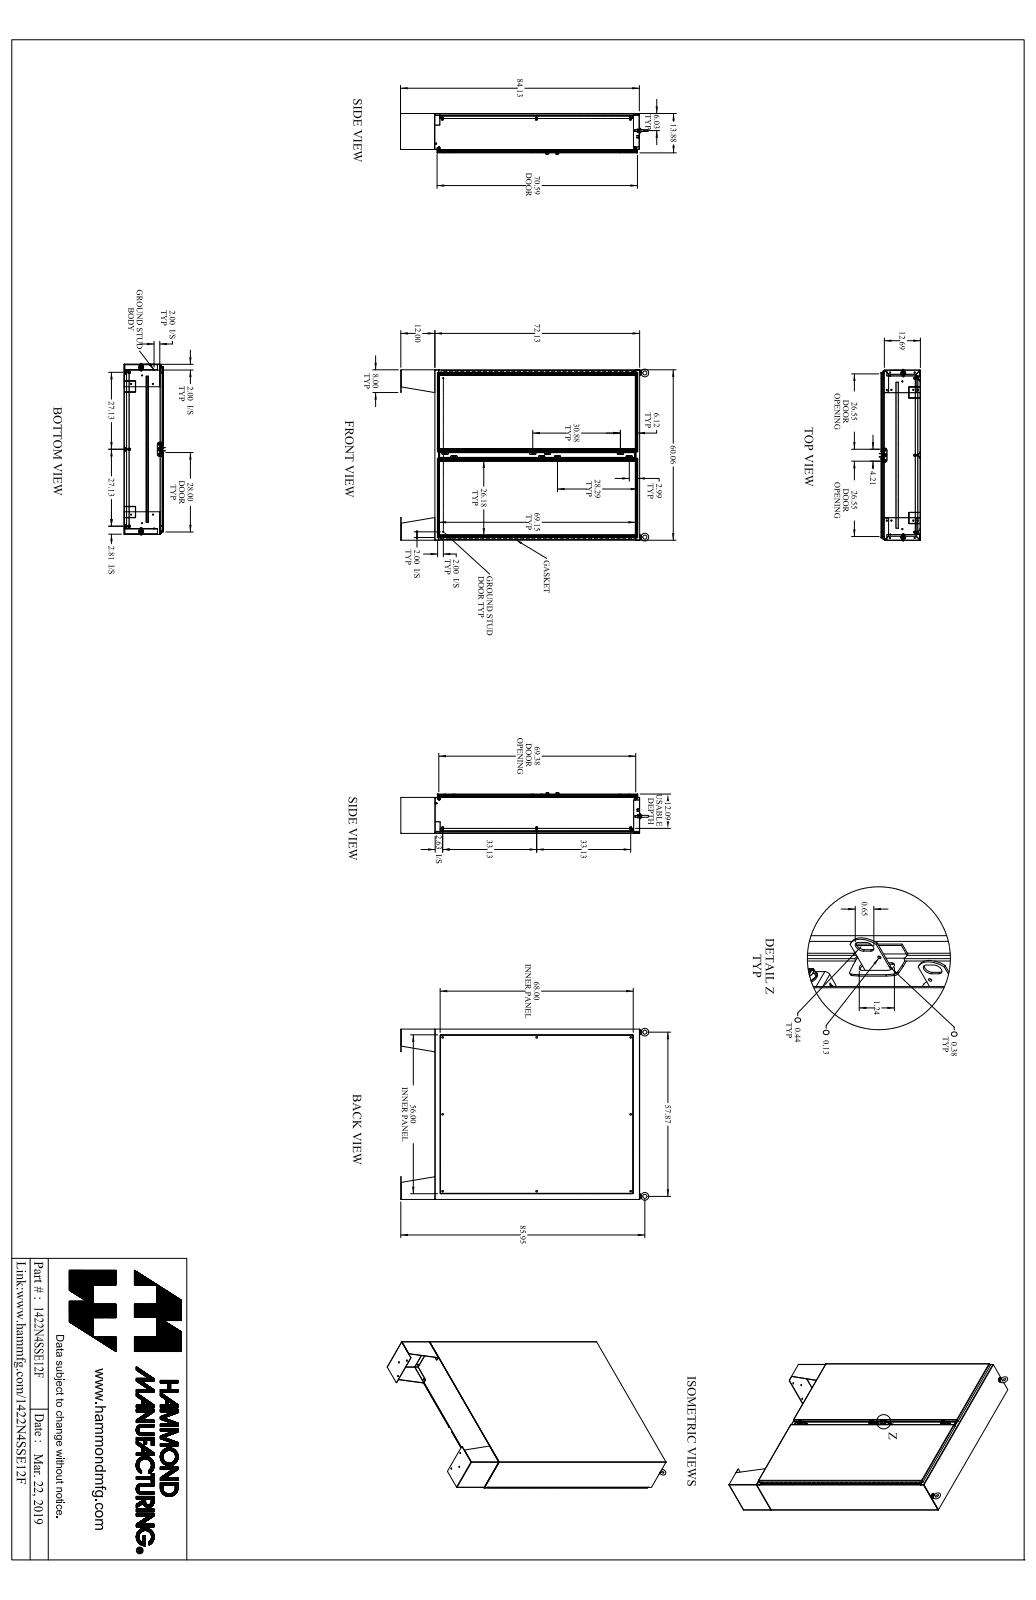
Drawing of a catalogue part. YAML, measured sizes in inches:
part_name: "1422N4SSE12F_Default"
step_written_by: "SolidWorks 2019 (CONFIG_CONTROL_DESIGN)"
units: inches
bodies: {solids: 107, faces: 3616, planar: 1838, cylindrical: 1582, other: 196}
overall_size: [87.784, 61.121, 14.468]
volume: 1973
surface_area: 39665
round_holes:
  - {diameter: 0.304, count: 24}
  - {diameter: 0.437, count: 14}
  - {diameter: 0.307, count: 8}
  - {diameter: 0.563, count: 8}
  - {diameter: 0.213, count: 6}
  - {diameter: 0.265, count: 6}
  - {diameter: 0.375, count: 6}
  - {diameter: 0.445, count: 6}
  - {diameter: 0.201, count: 3}
  - {diameter: 0.25, count: 3}
  - {diameter: 0.313, count: 3}
  - {diameter: 0.11, count: 2}
round_bosses_or_shafts:
  - {diameter: 1, count: 8}
  - {diameter: 0.65, count: 8}
  - {diameter: 0.375, count: 8}
  - {diameter: 0.332, count: 8}
  - {diameter: 0.5, count: 6}
  - {diameter: 0.39, count: 6}
  - {diameter: 0.244, count: 6}
  - {diameter: 0.313, count: 4}
partial_cylinders:
  - {radius: 0.048, count: 67}
  - {radius: 0.143, count: 67}
  - {radius: 0.25, count: 34}
  - {radius: 0.06, count: 18}
  - {radius: 0.116, count: 12}
  - {radius: 0.141, count: 12}
  - {radius: 0.185, count: 12}
  - {radius: 0.187, count: 11}
face_to_face_distances: [0.095, 13.78, 13.685, 13.875, 0.125, 11.998, 12.093, 1.687, 1.782, 12.218]
hole_center_spacings: [6, 58.513, 12, 59.429, 18, 60.924, 24, 62.959]
